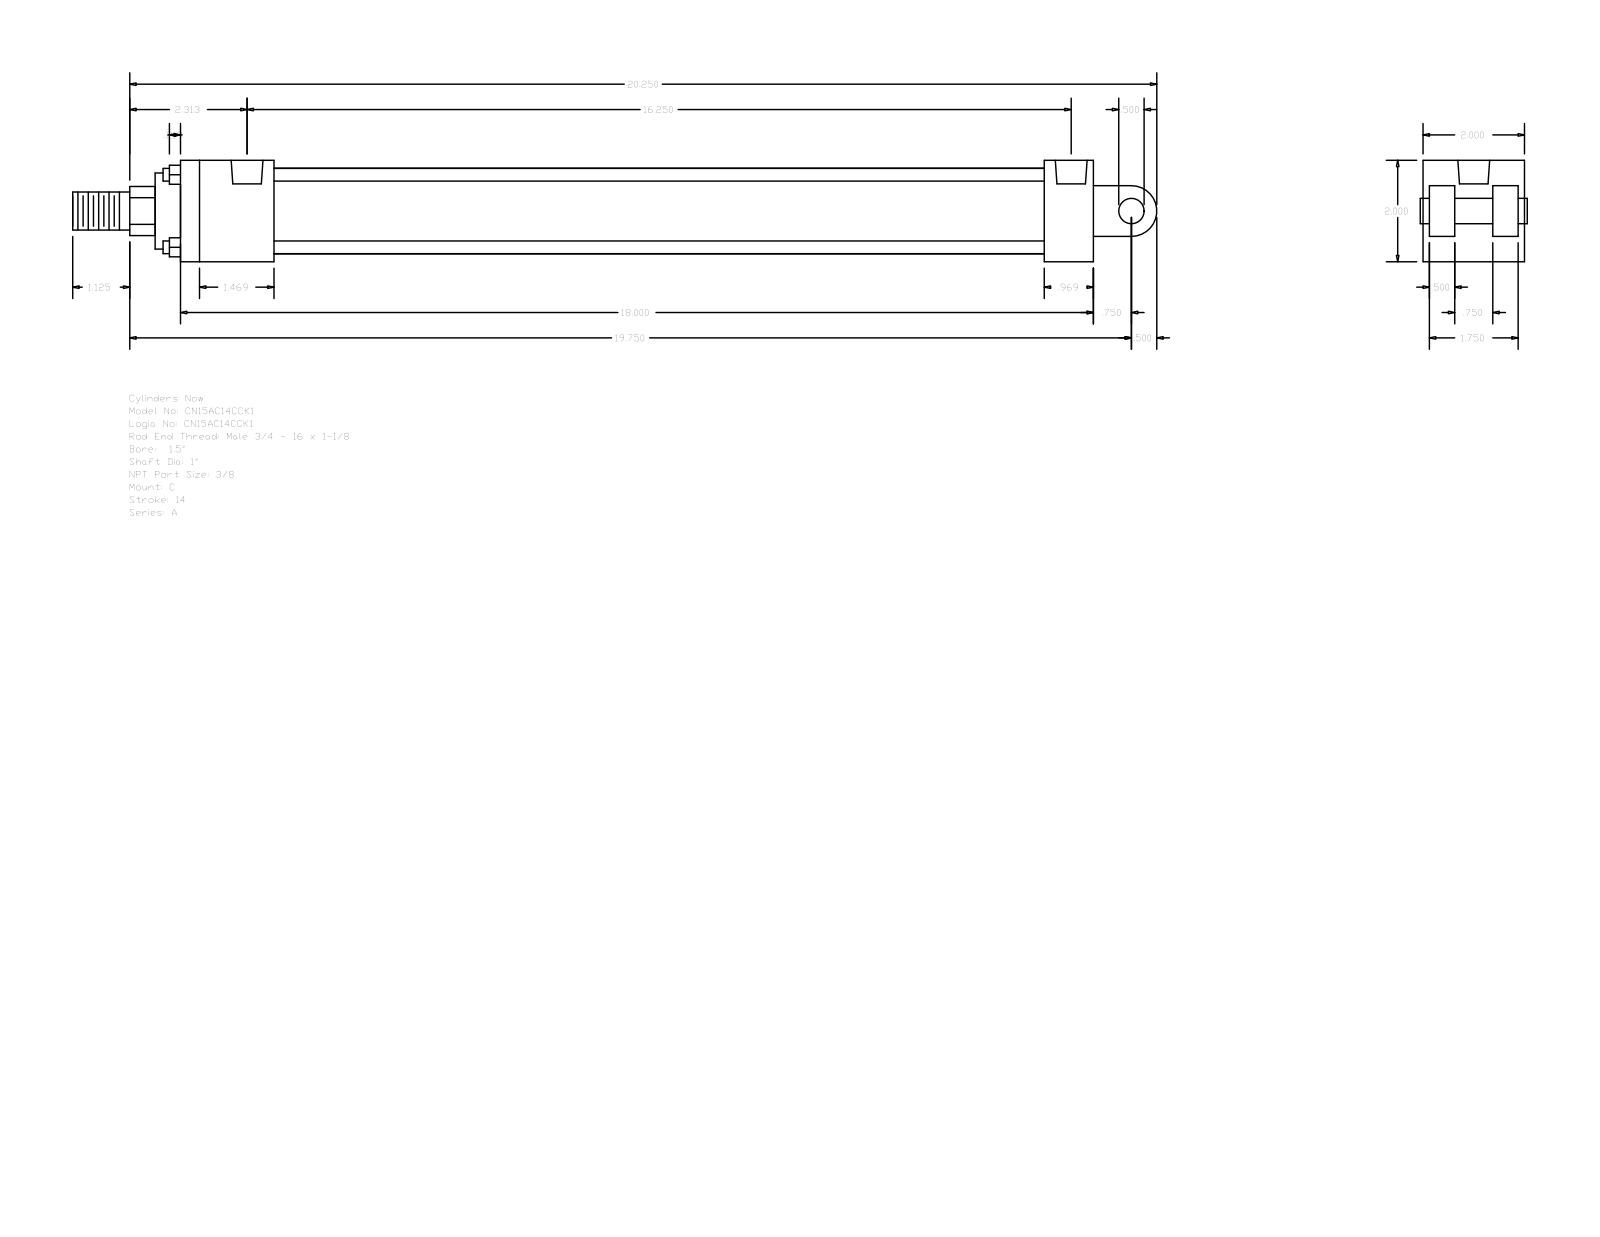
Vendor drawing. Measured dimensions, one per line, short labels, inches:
name: A_C__0150_1
written by: GSSL Pune (CONFIG_CONTROL_DESIGN)
unit: in
bodies: 0 solids, 99 faces (70 planar, 29 cylindrical, 0 other)
size: 21.375 × 2 × 2
holes: 4× ⌀0.219, 2× ⌀0.627
bosses: 4× ⌀0.25, 1× ⌀1.69, 1× ⌀1.5, 1× ⌀1, 1× ⌀0.75, 1× ⌀0.5
rounds: 1× R0.484, 1× R0.5
face distances: 2, 0.5, 0.125, 0.625, 1.375, 1.875, 1.25, 18, 1.5, 17.031
hole spacings: 0.156, 15.937, 16.094, 16.25
